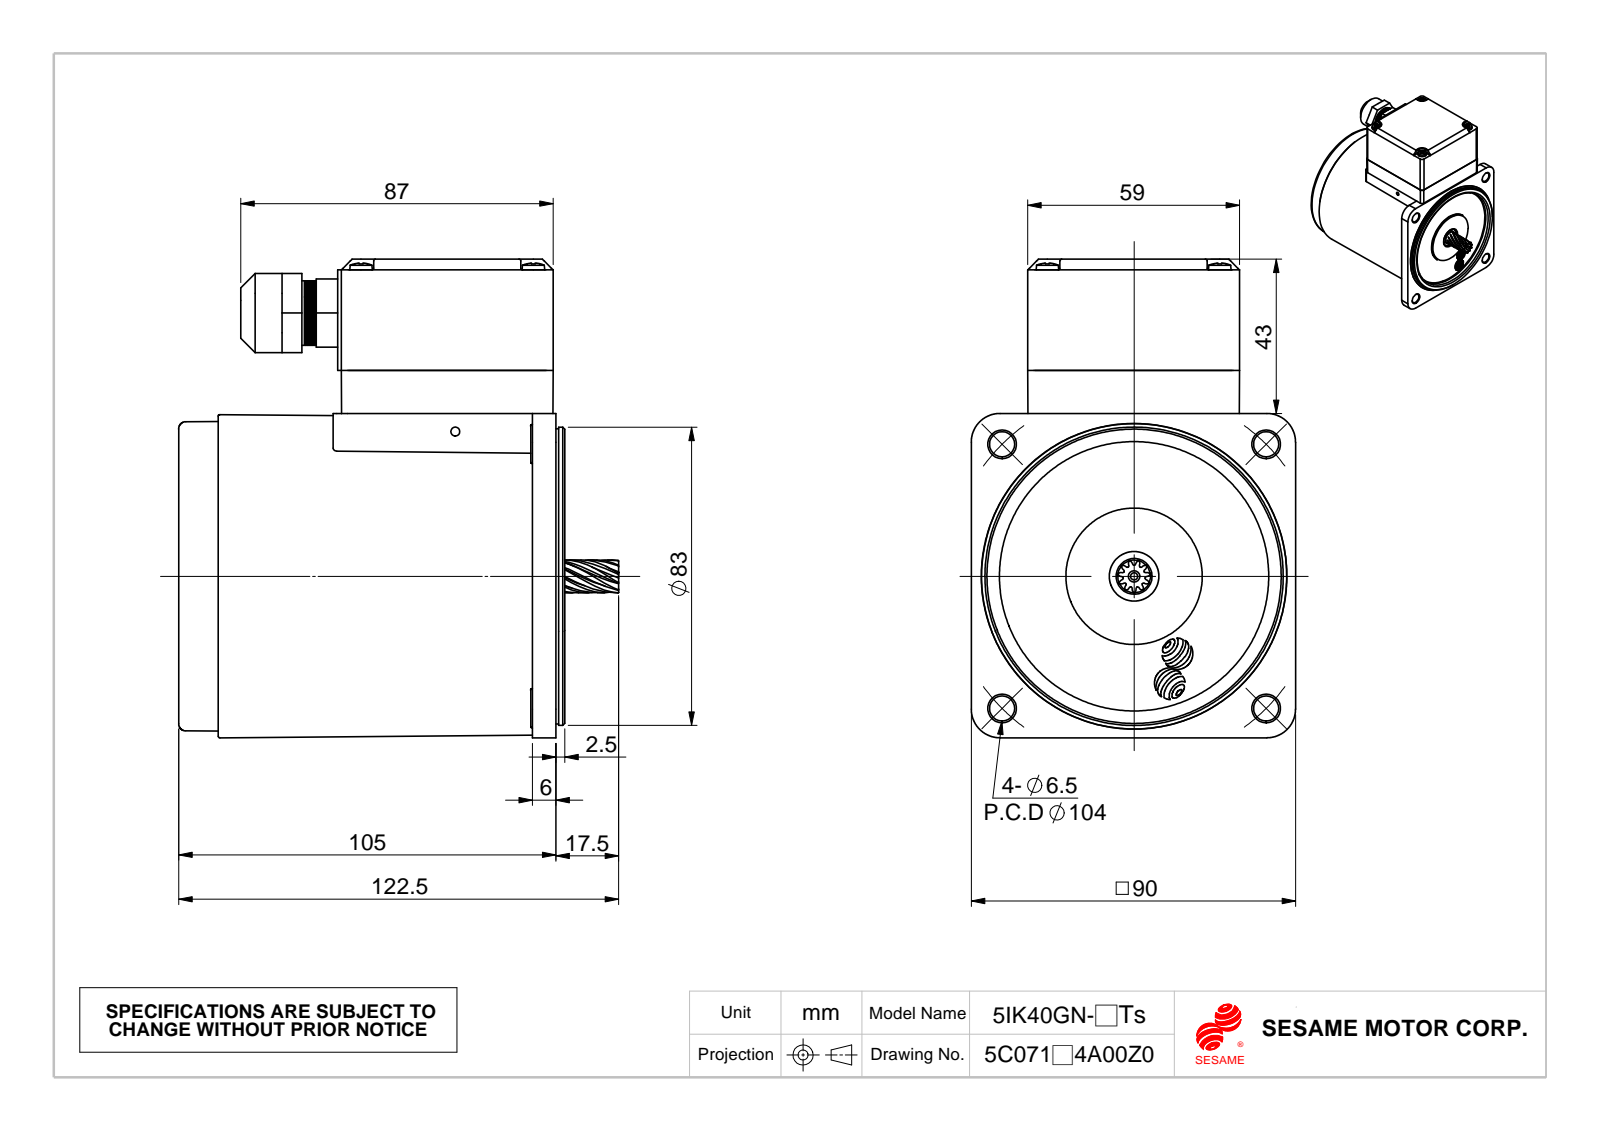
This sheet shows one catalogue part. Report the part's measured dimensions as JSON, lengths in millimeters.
{"part_name": "Ts下墊片; M540Ts; 成品180度; 40GN", "step_written_by": "SolidWorks 2010 (CONFIG_CONTROL_DESIGN)", "units": "millimeters", "bodies": {"solids": 11, "faces": 2577, "planar": 208, "cylindrical": 938, "other": 1431}, "overall_size": [133.3, 122.5, 90.3], "volume_mm3": 306848, "surface_area_mm2": 125165, "round_holes": [[3.3, 4], [3.5, 4], [3.9, 4], [4.3, 4], [7, 4], [2, 1], [2.5, 1], [11, 1], [12, 1], [13.7, 1], [14.5, 1], [21, 1]], "round_bosses_or_shafts": [[6.3, 4], [3, 4], [84.22, 1], [83, 1], [82.2, 1], [38, 1], [35, 1], [22, 1]], "partial_cylinders_radius": [[2, 12], [0.5, 8], [0.78, 8], [1.5, 8], [1.66, 8], [2.92, 8], [4, 6], [0.2, 4]], "face_to_face_distances": [1, 12, 102.5, 98, 103.5, 1.5, 2.5, 99, 0.75, 101.5], "hole_center_spacings": [48, 52, 73.54, 11.67, 12.35, 12.7, 24.93, 25]}
